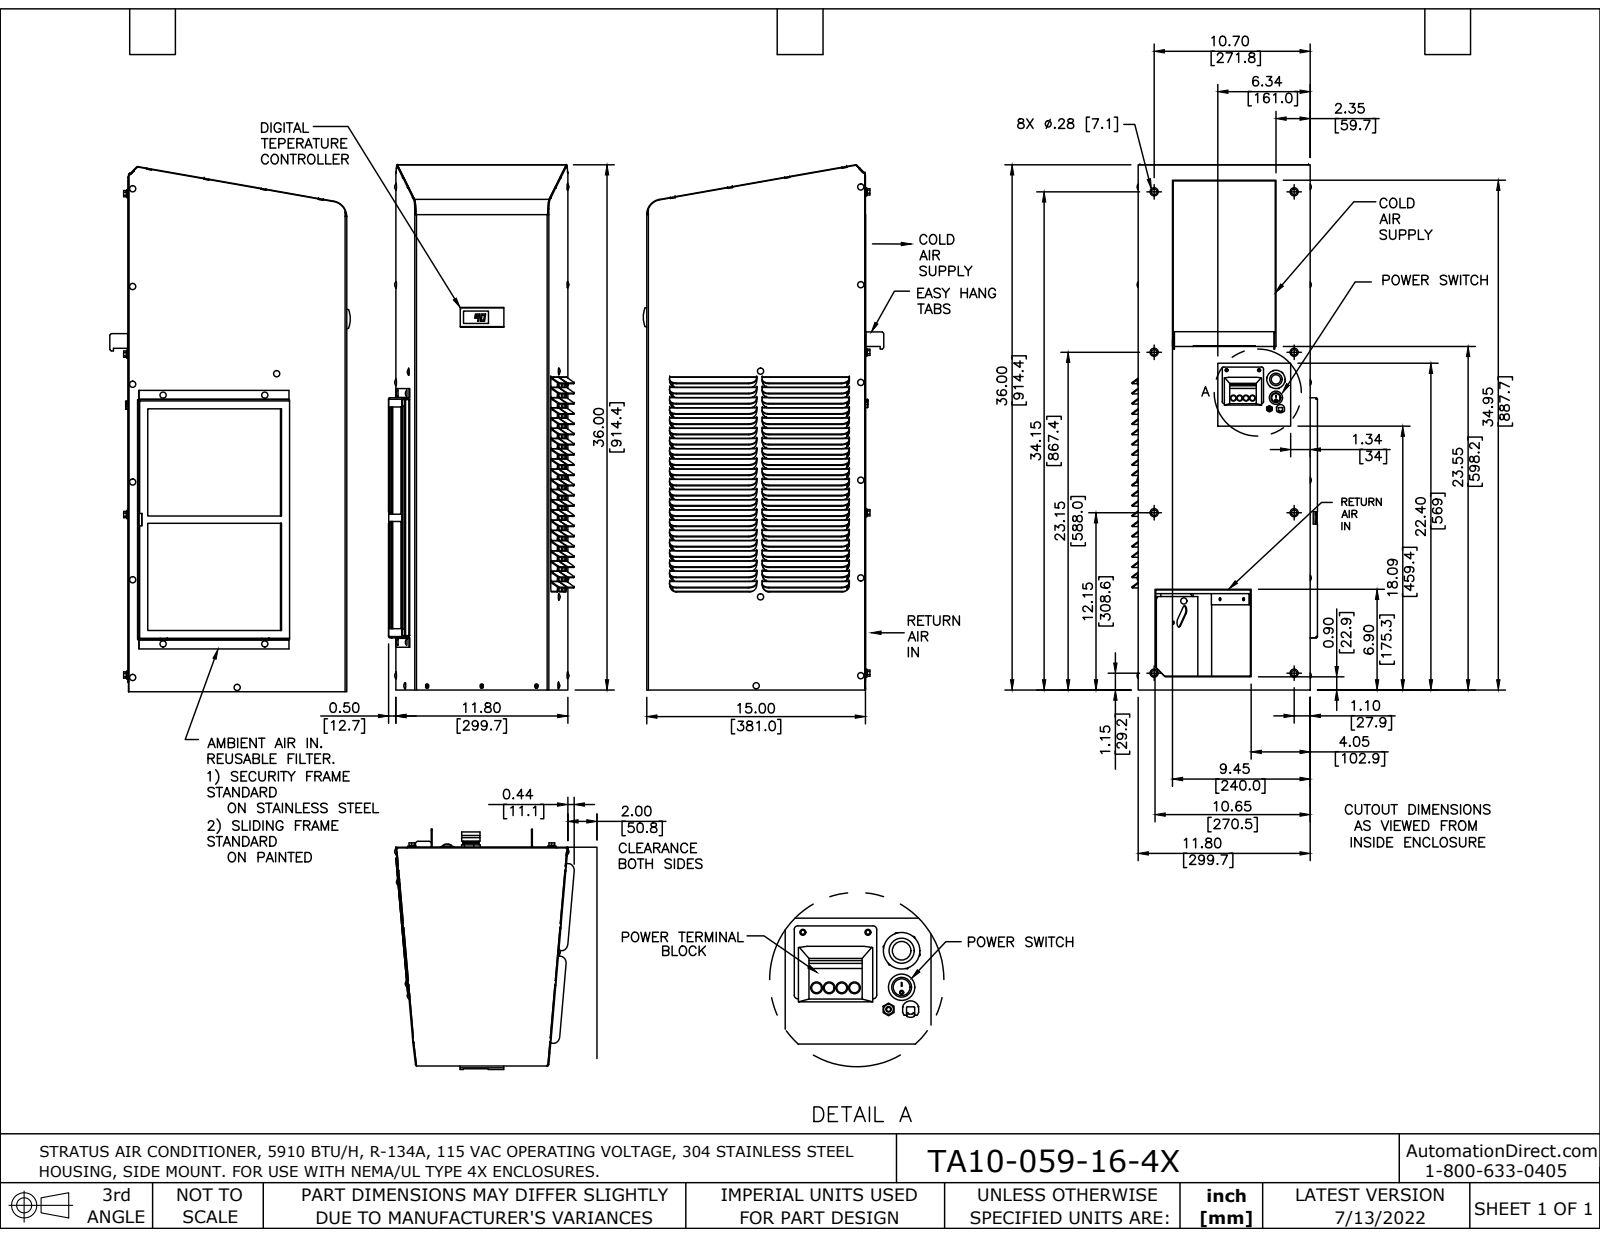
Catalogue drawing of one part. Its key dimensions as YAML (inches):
part_name: "NE050-~1"
step_written_by: "SolidWorks 2021 (AUTOMOTIVE_DESIGN)"
units: inches
bodies: {solids: 50, faces: 3771, planar: 2045, cylindrical: 1437, other: 289}
overall_size: [36.003, 17.4, 13.814]
volume: 212
surface_area: 5596
round_holes:
  - {diameter: 0.194, count: 8}
  - {diameter: 0.25, count: 6}
  - {diameter: 0.277, count: 6}
  - {diameter: 0.228, count: 4}
  - {diameter: 0.082, count: 2}
  - {diameter: 0.091, count: 2}
  - {diameter: 0.204, count: 2}
  - {diameter: 0.156, count: 1}
  - {diameter: 0.201, count: 1}
  - {diameter: 0.21, count: 1}
  - {diameter: 0.375, count: 1}
  - {diameter: 0.64, count: 1}
round_bosses_or_shafts:
  - {diameter: 0.366, count: 34}
  - {diameter: 0.17, count: 34}
  - {diameter: 1.254, count: 1}
  - {diameter: 1.236, count: 1}
  - {diameter: 1.098, count: 1}
  - {diameter: 0.906, count: 1}
  - {diameter: 0.19, count: 1}
  - {diameter: 0.064, count: 1}
partial_cylinders:
  - {radius: 0.019, count: 204}
  - {radius: 0.019, count: 204}
  - {radius: 0.031, count: 90}
  - {radius: 0.5, count: 88}
  - {radius: 0.506, count: 88}
  - {radius: 0.594, count: 86}
  - {radius: 0.089, count: 61}
  - {radius: 0.03, count: 47}
face_to_face_distances: [0.058, 14.948, 15.002, 14.944, 15.006, 14.89, 0.054, 15.044, 14.986, 0.096]
hole_center_spacings: [11, 6.1, 9.6, 14.6, 17.05, 17.05, 22, 7.609]
